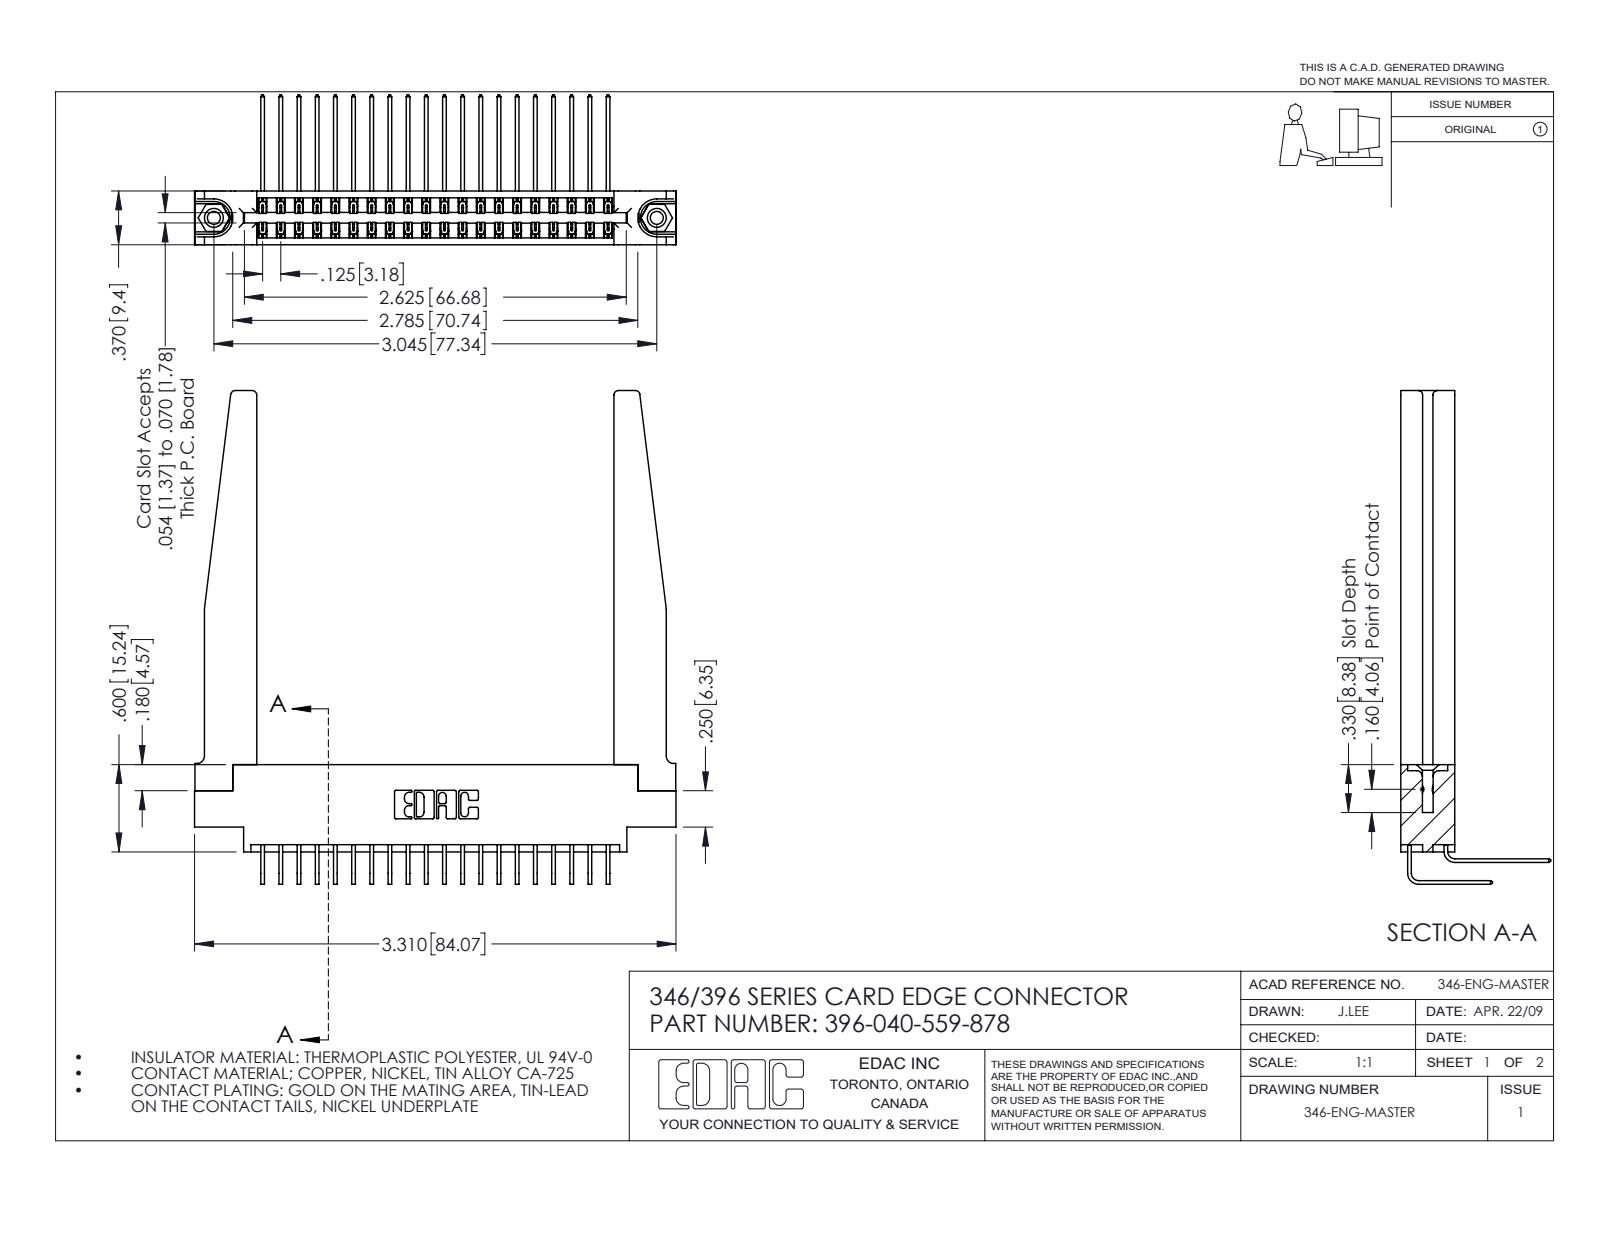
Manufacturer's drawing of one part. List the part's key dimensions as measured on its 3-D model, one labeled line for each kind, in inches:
Part name (STEP PRODUCT): 345-292-001_559 Tail - 2; 345-292-001_558 559 Tail - 1; 346-220-078_345-220-078; 396-040-559-878 (+2 more)
STEP written by: SolidWorks 2016 (CONFIG_CONTROL_DESIGN)
Units: inches
Bodies: 45 solids, 2520 faces (1702 planar, 766 cylindrical, 52 other)
Overall size (bounding box): 3.393 × 3.31 × 1.03
Volume: 0.916 in³ · Surface area: 28.86 in²
Round holes (diameter × count): ⌀0.089 ×2, ⌀0.125 ×2, ⌀0.156 ×2, ⌀0.064 ×1
Round bosses / shafts (diameter × count): ⌀0.155 ×2
Partial cylindrical surfaces — rounded edges, fillets, slot ends (radius × count): R0.006 ×60, R0.01 ×22, R0.03 ×8, R0.007 ×6, R0.031 ×6, R0.05 ×4, R0.026 ×3, R0.014 ×2
Main face-to-face distances: 0.37, 0.048, 0.072, 0.322, 0.148, 0.15, 0.025, 0.25, 0.298, 0.275
Hole centre spacings: 0.246, 2.837, 3.045
